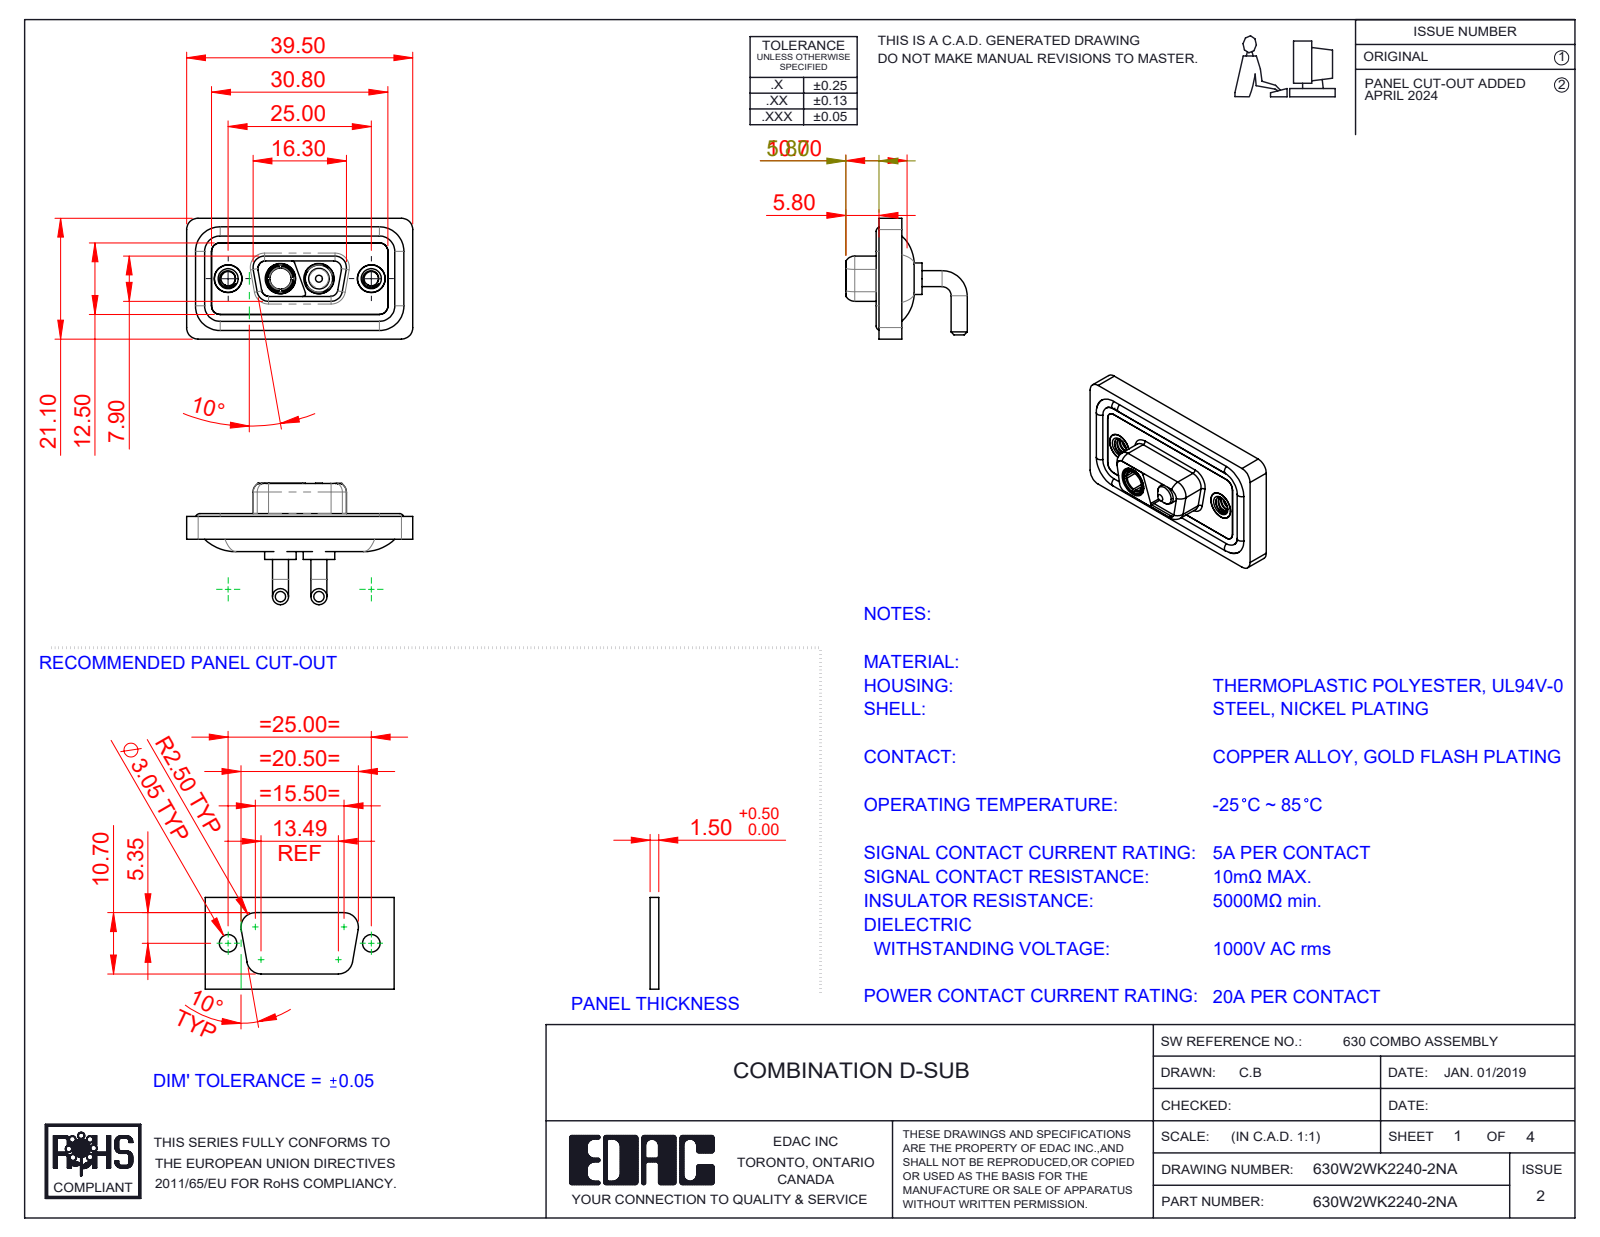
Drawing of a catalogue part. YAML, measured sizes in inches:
part_name: "630Combo Threaded Rivet_A; Power Socket_20A RA; 630W2WK2240-2NA; Power Pin_20A RA (+4 more)"
step_written_by: "SolidWorks 2023 (CONFIG_CONTROL_DESIGN)"
units: inches
bodies: {solids: 11, faces: 502, planar: 144, cylindrical: 233, other: 125}
overall_size: [1.555, 0.835, 0.831]
volume: 0.287
surface_area: 11.62
round_holes:
  - {diameter: 0.191, count: 4}
  - {diameter: 0.098, count: 2}
  - {diameter: 0.157, count: 2}
  - {diameter: 0.159, count: 2}
  - {diameter: 0.197, count: 2}
  - {diameter: 0.209, count: 2}
  - {diameter: 0.146, count: 1}
round_bosses_or_shafts:
  - {diameter: 0.11, count: 4}
  - {diameter: 0.063, count: 4}
  - {diameter: 0.217, count: 2}
  - {diameter: 0.205, count: 2}
  - {diameter: 0.195, count: 2}
  - {diameter: 0.189, count: 2}
  - {diameter: 0.187, count: 2}
  - {diameter: 0.148, count: 2}
partial_cylinders:
  - {radius: 0.059, count: 18}
  - {radius: 0.079, count: 18}
  - {radius: 0.053, count: 8}
  - {radius: 0.063, count: 8}
  - {radius: 0.02, count: 6}
  - {radius: 0.01, count: 4}
  - {radius: 0.024, count: 4}
  - {radius: 0.026, count: 4}
face_to_face_distances: [0.016, 0.043, 0.114, 0.071, 0.098, 0.063, 0.122, 0.059, 0.083, 0.146]
hole_center_spacings: [0.36, 0.624, 0.265, 0.984]
